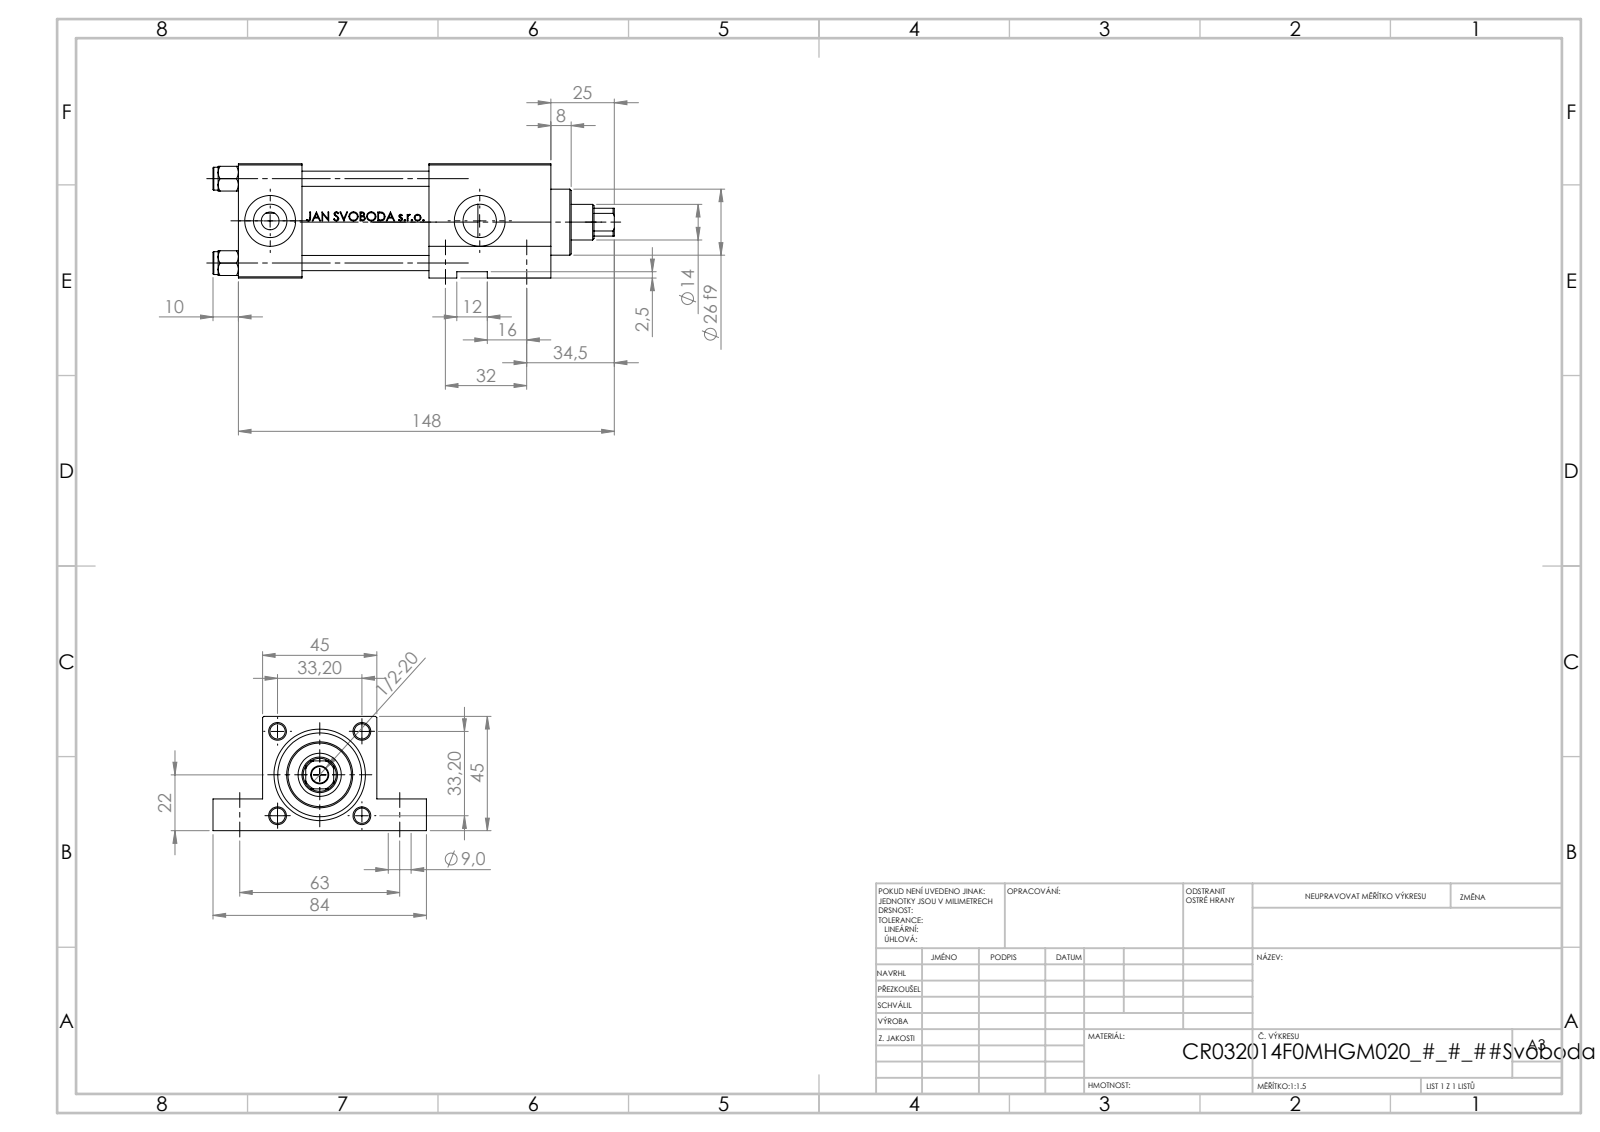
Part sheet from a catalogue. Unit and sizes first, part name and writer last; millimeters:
Units: millimetres
Overall size (bounding box): 158 × 84 × 45
Round holes (diameter × count): ⌀6 ×4, ⌀9 ×4, ⌀7 ×2, ⌀13.16 ×2, ⌀20 ×2, ⌀6.5 ×1, ⌀14 ×1, ⌀17 ×1, ⌀24 ×1, ⌀32 ×1, ⌀33 ×1
Round bosses / shafts (diameter × count): ⌀9 ×4, ⌀38 ×1, ⌀26 ×1
Partial cylindrical surfaces — rounded edges, fillets, slot ends (radius × count): R6.5 ×1
Main face-to-face distances: 45, 25, 98, 123, 50, 32.5, 75, 48, 12.5, 10
Hole centre spacings: 33.2, 23.13, 23.83, 32, 46.95, 63, 70.66, 82.5
Volume: 212 246 mm³ · Surface area: 72 585 mm²
Bodies: 11 solids, 1102 faces (436 planar, 126 cylindrical, 540 other)
Part name (STEP PRODUCT): NUT_M5_F; V215CR_F_Body; V215CR_F_TYCINKA; V215_VC_A (+1 more)
STEP written by: SolidWorks 2019 (CONFIG_CONTROL_DESIGN)
